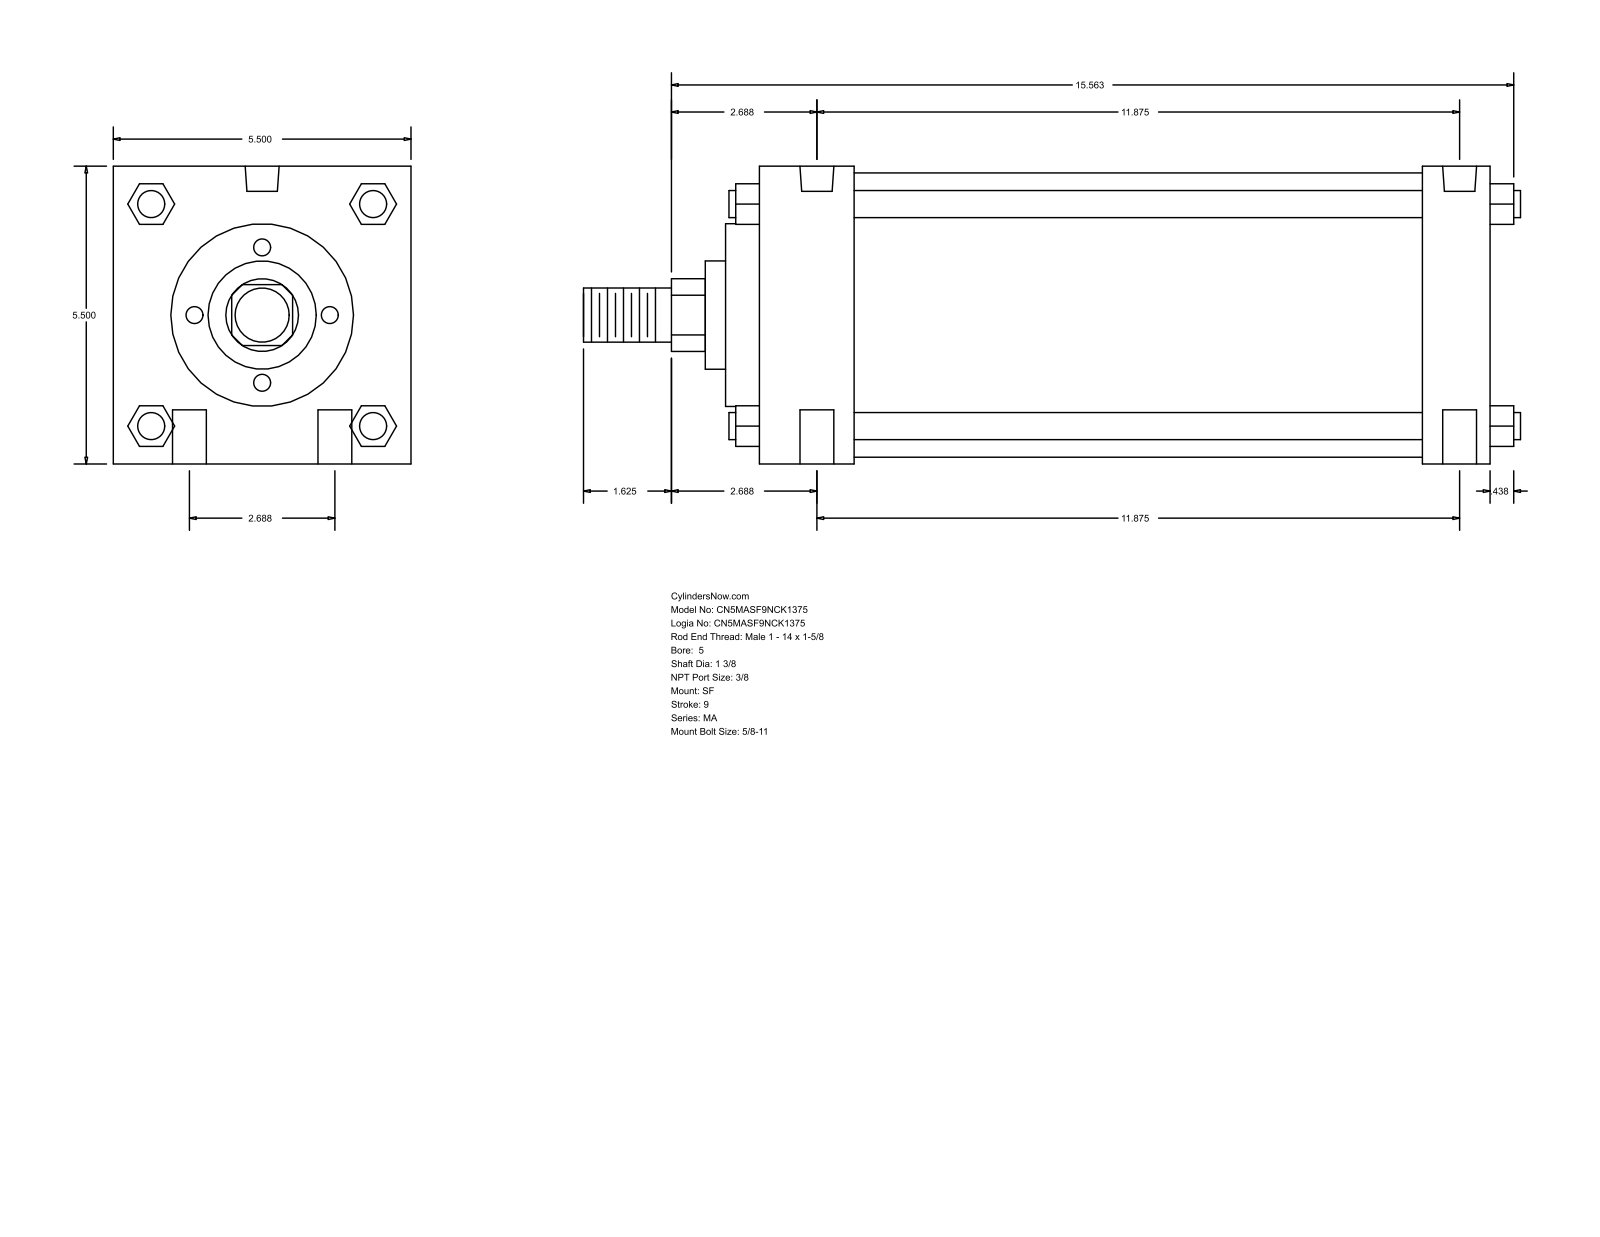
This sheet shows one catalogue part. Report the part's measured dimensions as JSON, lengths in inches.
{"part_name": "MA_SF__0500_1.375", "step_written_by": "GSSL Pune (CONFIG_CONTROL_DESIGN)", "units": "inches", "bodies": {"solids": 0, "faces": 126, "planar": 95, "cylindrical": 31, "other": 0}, "overall_size": [17.313, 5.5, 5.5], "round_holes": [[0.625, 4], [0.437, 2], [0.627, 2]], "round_bosses_or_shafts": [[0.5, 4], [5.25, 1], [3.375, 1], [2, 1], [1.375, 1], [1, 1]], "partial_cylinders_radius": [[0.672, 1]], "face_to_face_distances": [5.5, 13.5, 1.75, 12.25, 10.5, 11.75, 1.25, 0.625, 2.375, 12.875], "hole_center_spacings": [1.344, 11.951, 11.875, 2.687, 12.176, 11.5]}
